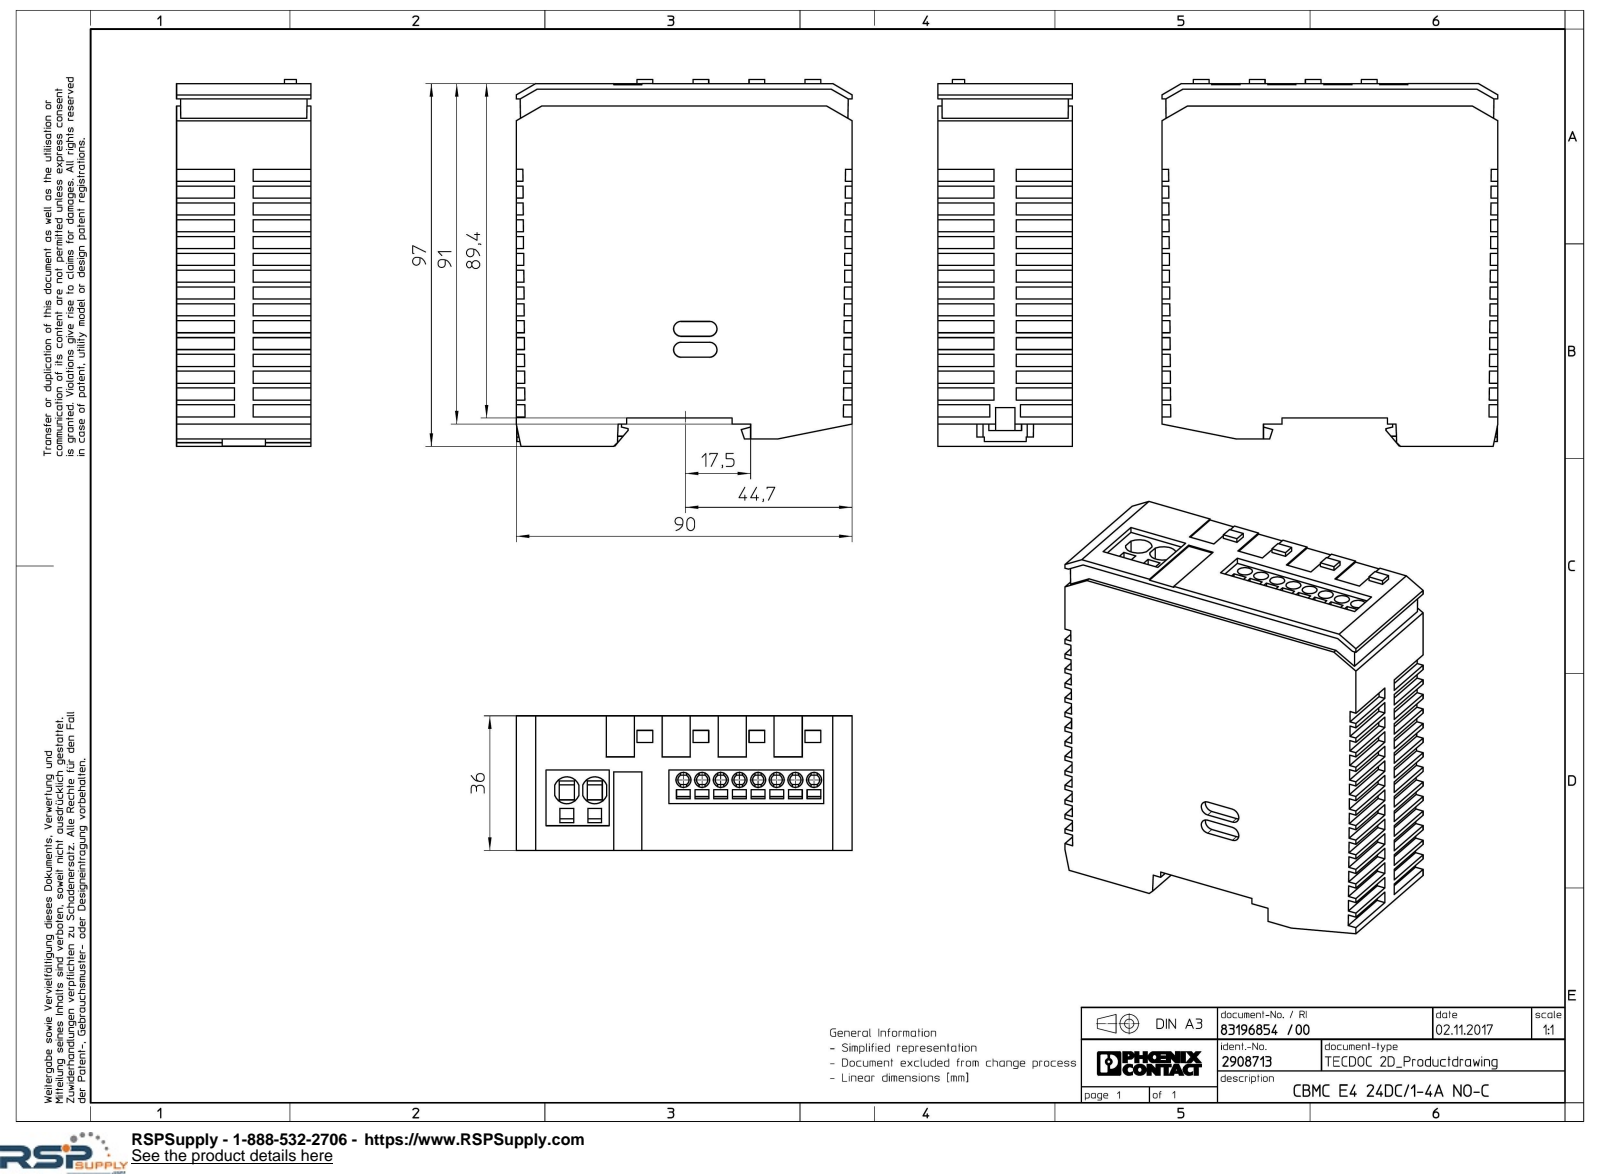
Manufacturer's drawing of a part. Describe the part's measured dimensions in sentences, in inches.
The part is named "CBMC_E4_24DC...NO-select". Its 3-D file was written by "Creo Elements/Direct Modeling 18.1I 14-Aug-2016 (C) Parametric Technology GmbH (AUTOMOTIVE_DESIGN)". It is 1 solid with 533 faces: 491 planar, 22 cylindrical and 20 other. Overall it measures 3.862 by 3.543 by 1.417 inches. Its volume is 17.73 cubic inches and its surface area 56.42 square inches. Round holes: 8 of diameter 0.157. Partial cylindrical surfaces (rounded edges, fillets, slot ends): 4 of radius 0.136, 1 of radius 0.472. The main face-to-face distances are 1.417, 3.543, 3.52, 0.177, 0.299, 3.819, 0.354, 0.128, 0.05, 3.807. The hole center spacings are 0.197, 0.394, 0.591, 0.787, 0.984, 1.181, 1.378.
